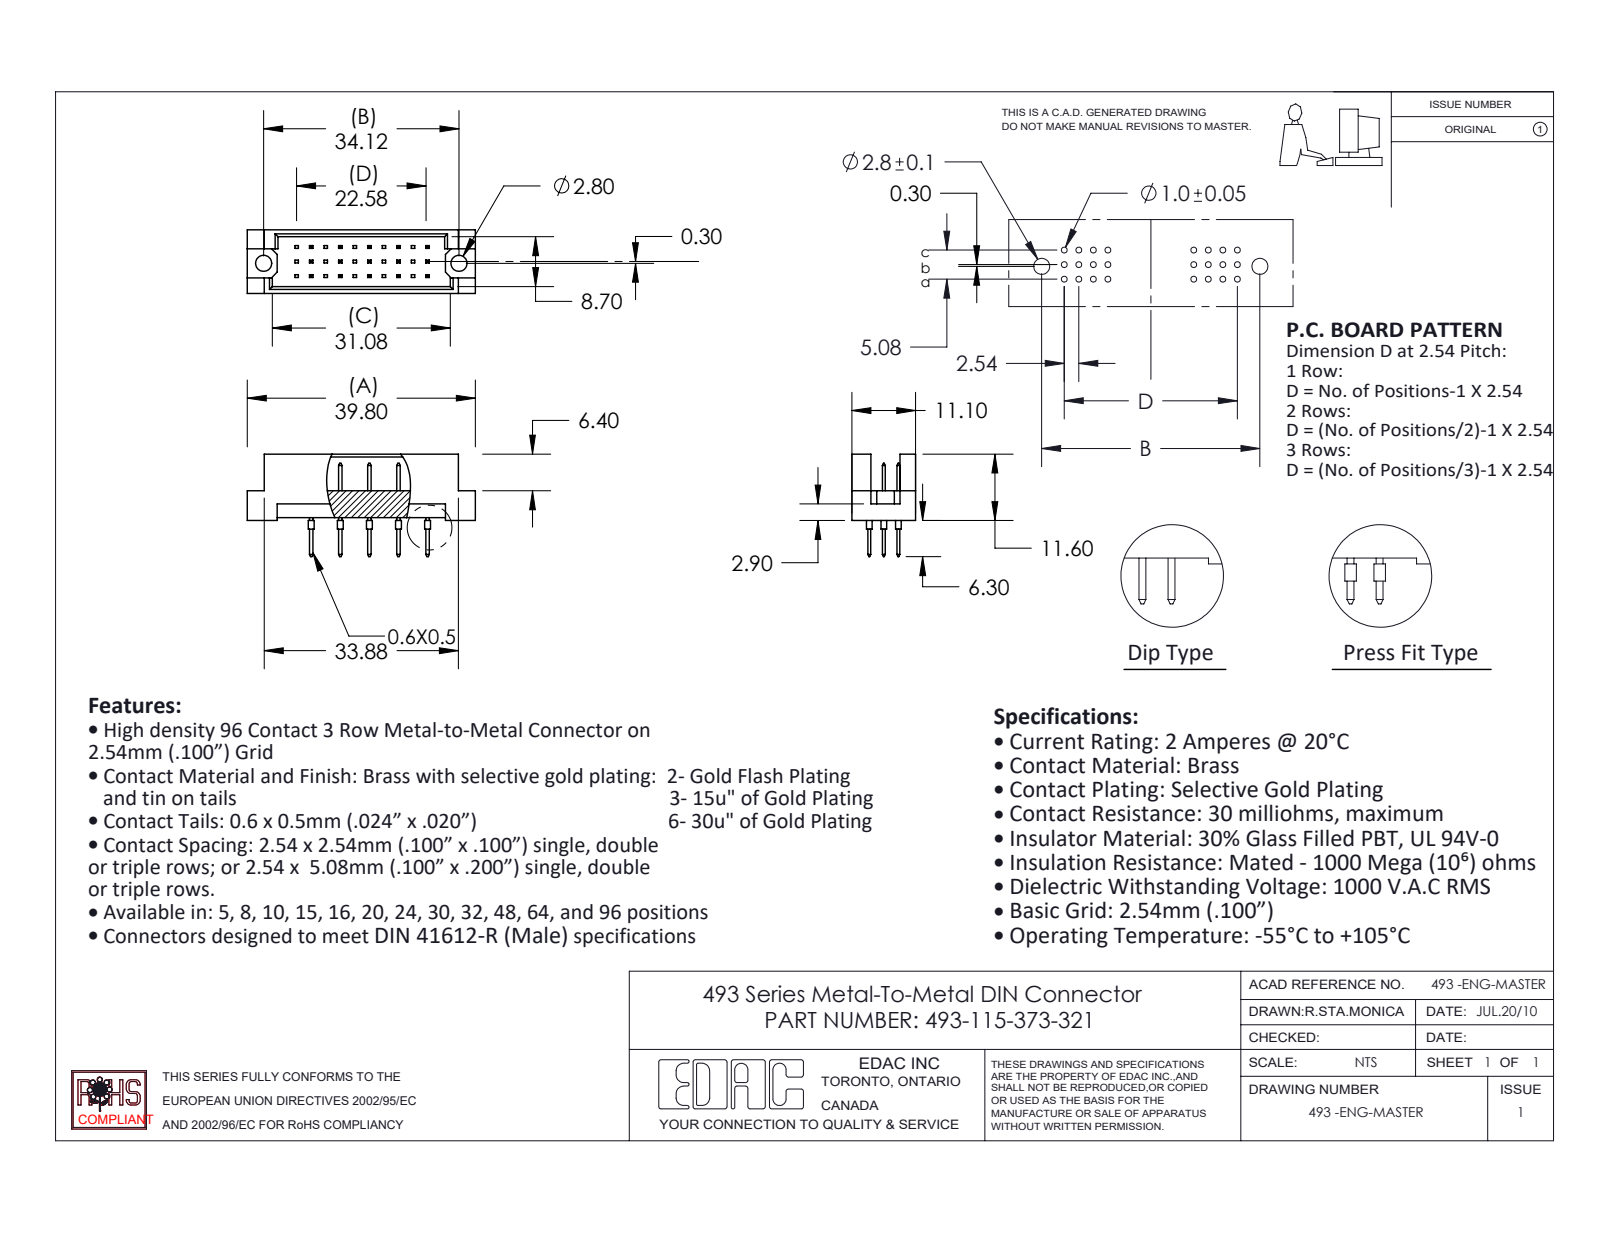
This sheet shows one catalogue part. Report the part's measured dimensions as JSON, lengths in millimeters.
{"part_name": "493-290_73; 493-115-373-322; 493 Part_30", "step_written_by": "SolidWorks 2020 (CONFIG_CONTROL_DESIGN)", "units": "millimeters", "bodies": {"solids": 16, "faces": 502, "planar": 468, "cylindrical": 34, "other": 0}, "overall_size": [39.8, 17.9, 11.1], "volume_mm3": 2456, "surface_area_mm2": 3306, "round_holes": [[2.8, 2]], "round_bosses_or_shafts": [[1, 15]], "face_to_face_distances": [1.2, 9.9, 5.08, 11.1, 0.5, 8.7, 2.54, 4.7, 10.16, 2.76], "hole_center_spacings": [34.12]}
